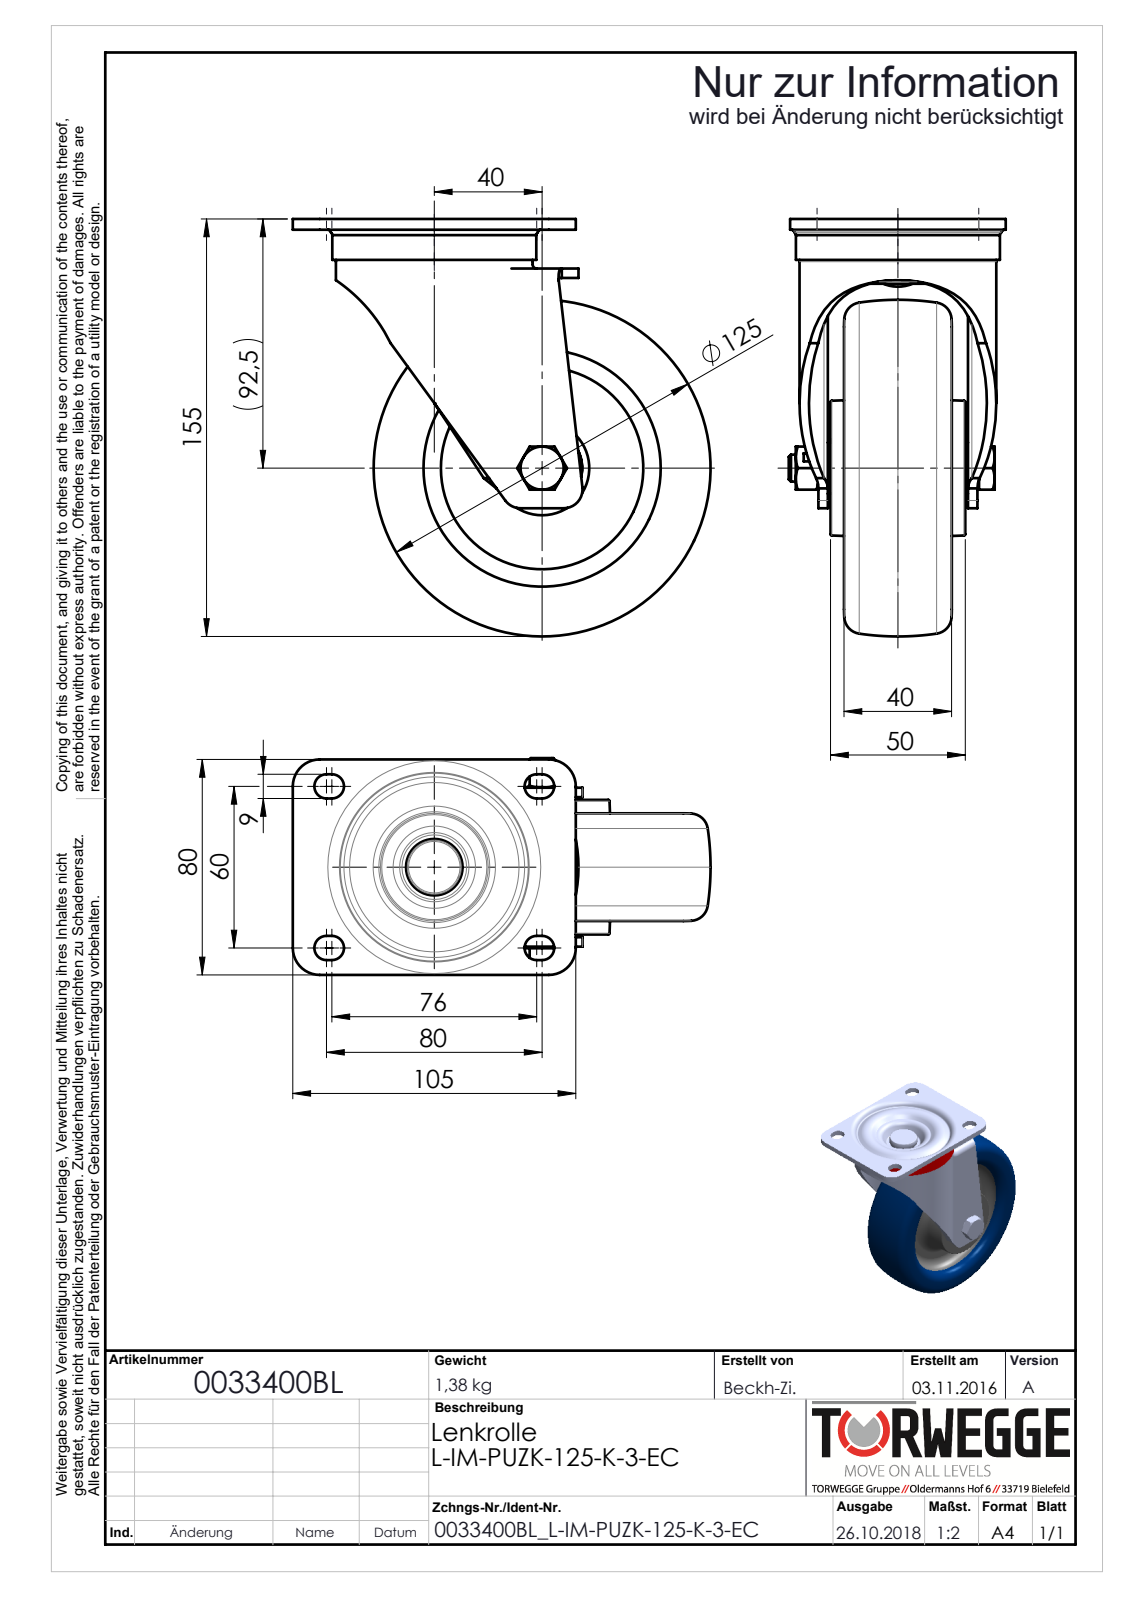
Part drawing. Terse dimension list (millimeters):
name: 0033400_L-IM-PUZK-125-K-3-EC
written by: SolidWorks 2016 (AUTOMOTIVE_DESIGN)
unit: mm
bodies: 0 solids, 701 faces (314 planar, 168 cylindrical, 219 other)
size: 155 × 155 × 80.5
holes: 1× ⌀8.5, 1× ⌀10, 1× ⌀10.35, 1× ⌀10.5, 1× ⌀12.5, 1× ⌀15, 1× ⌀16, 1× ⌀29.7, 1× ⌀35, 1× ⌀35.1, 1× ⌀36, 1× ⌀46.75
bosses: 1× ⌀75.69, 1× ⌀73, 1× ⌀52.5, 1× ⌀21, 1× ⌀19.75, 1× ⌀14.9, 1× ⌀12.5
rounds: 10× R4.5, 8× R0.37, 7× R0.21, 7× R0.62, 4× R0.12, 4× R0.86, 4× R0.93, 4× R10
face distances: 3.5, 1, 4, 55.5, 54.5, 4.5, 51, 59, 52, 24.5
